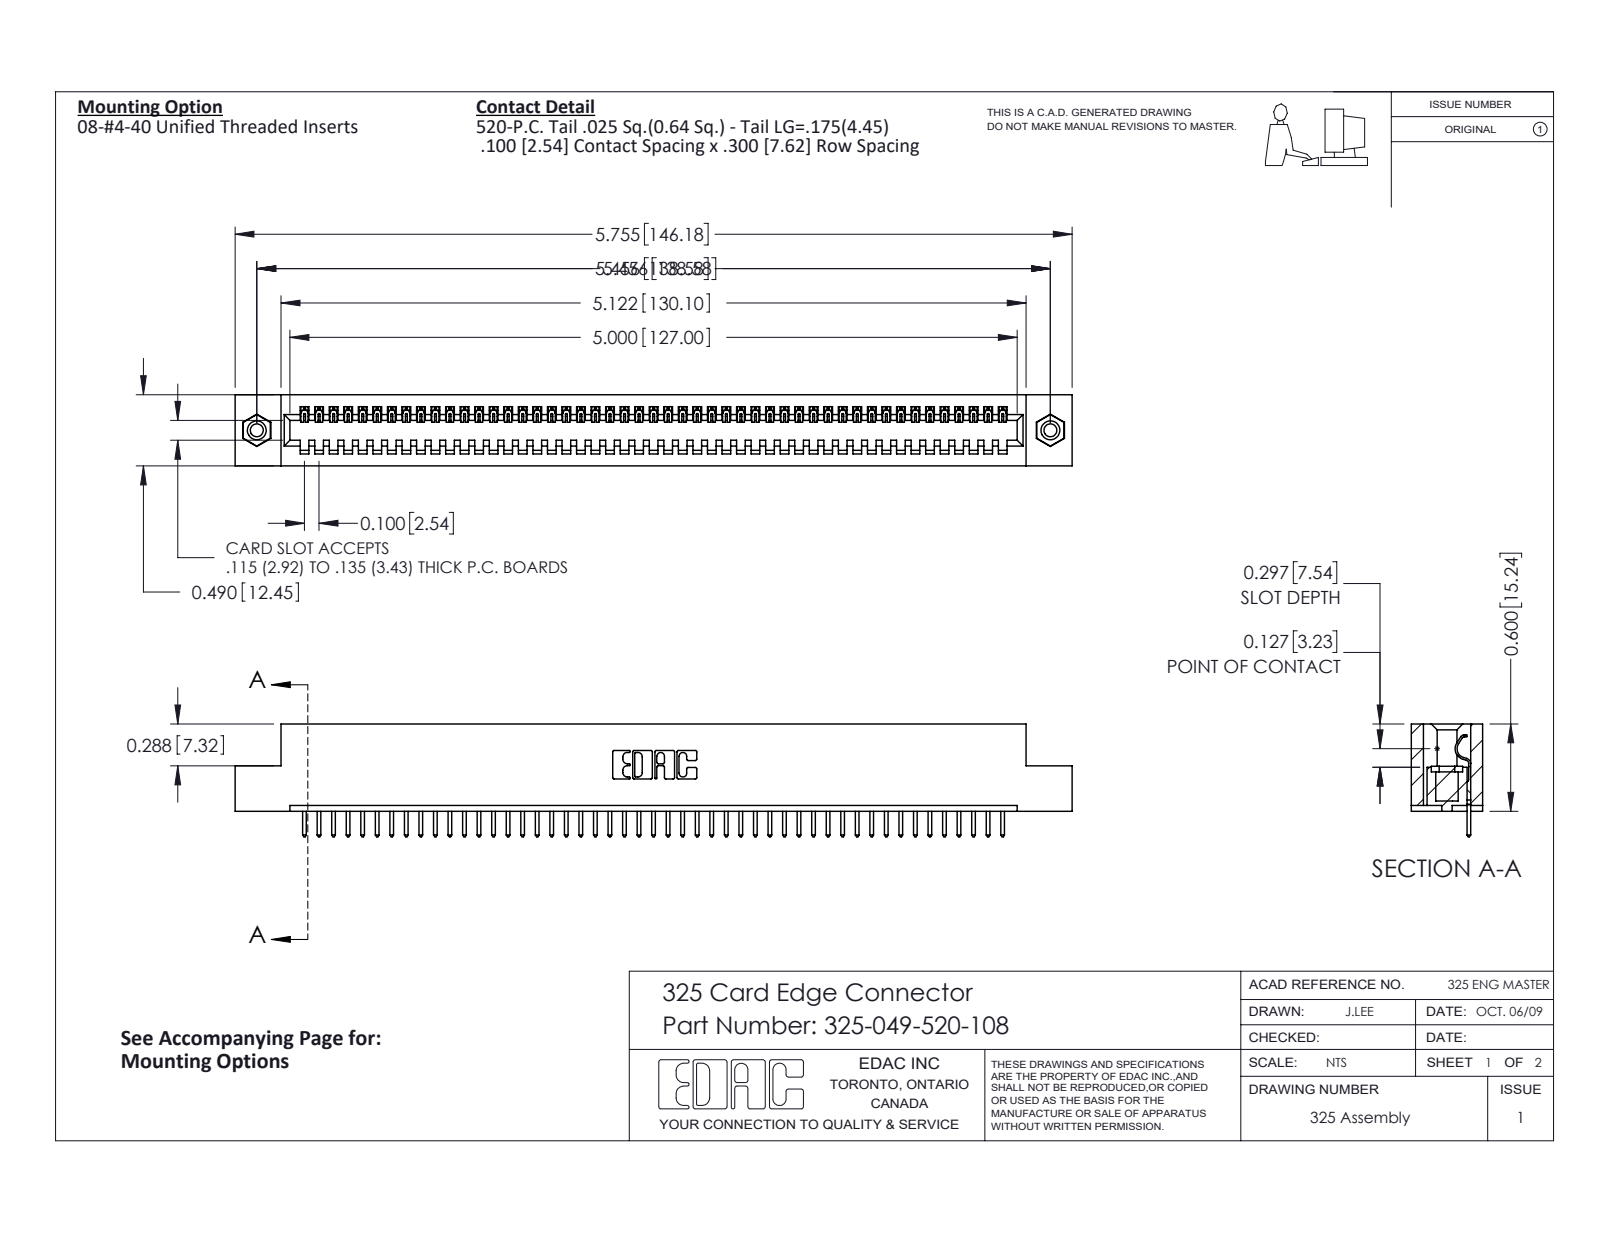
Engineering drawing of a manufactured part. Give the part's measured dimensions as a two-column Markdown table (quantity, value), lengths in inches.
| quantity | value |
| --- | --- |
| part name | 325 Part_TI; 345-250-001_345-250-003-102; 325-049-520-108; 325-292-001_325-293-120 |
| STEP written by | SolidWorks 2016 (CONFIG_CONTROL_DESIGN) |
| units | inches |
| bodies | 52 solids, 3016 faces (2160 planar, 840 cylindrical, 16 other) |
| overall size | 5.755 × 0.775 × 0.49 |
| volume | 1.128 in³ |
| surface area | 30.7 in² |
| round holes (diameter × count) | 0.089 × 2, 0.125 × 2, 0.16 × 2 |
| round bosses / shafts (diameter × count) | 0.155 × 2 |
| partial cylindrical surfaces (radius × count) | 0.006 × 98, 0.01 × 98, 0.01 × 22, 0.007 × 6, 0.031 × 6, 0.026 × 3, 0.014 × 1, 0.022 × 1 |
| main face-to-face distances | 0.083, 0.407, 0.49, 0.3, 0.107, 0.383, 0.025, 0.325, 0.56, 0.263 |
| hole center spacings | 5.456 |
